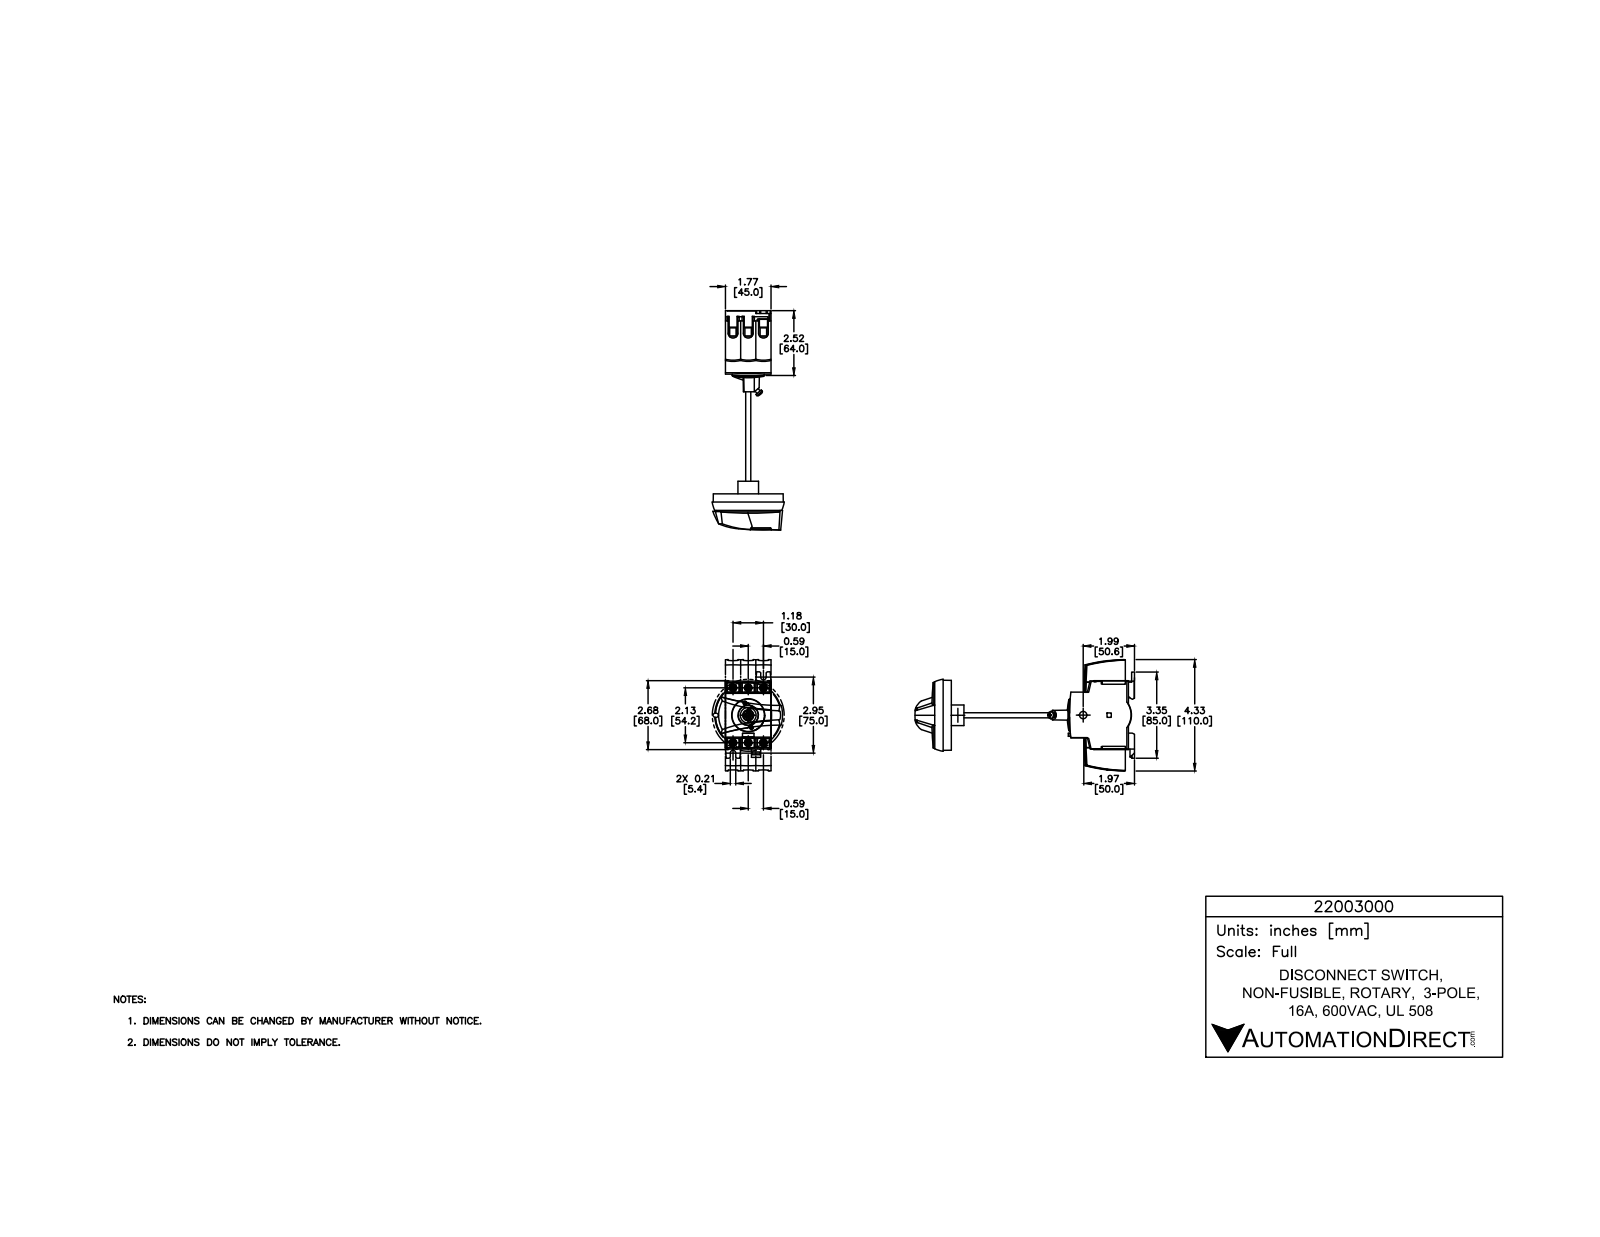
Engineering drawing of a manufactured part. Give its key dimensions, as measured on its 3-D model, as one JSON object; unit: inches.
{"part_name": "22003000-UL", "step_written_by": "SolidWorks 2021 (CONFIG_CONTROL_DESIGN)", "units": "inches", "bodies": {"solids": 1, "faces": 463, "planar": 389, "cylindrical": 50, "other": 24}, "overall_size": [3.346, 2.571, 1.772], "volume_in3": 9.498, "surface_area_in2": 40.23, "round_holes": [[0.26, 6], [0.283, 1], [1.244, 1]], "partial_cylinders_radius": [[0.012, 13], [0.02, 5], [0.165, 4], [0.039, 3], [0.106, 2], [0.13, 1], [0.354, 1], [0.37, 1]], "face_to_face_distances": [1.772, 0.433, 2.205, 2.157, 2.638, 2.28, 0.591, 2.591, 0.047, 0.386], "hole_center_spacings": [0.591, 1.219, 2.214, 2.134, 1.067, 1.181, 2.439]}
